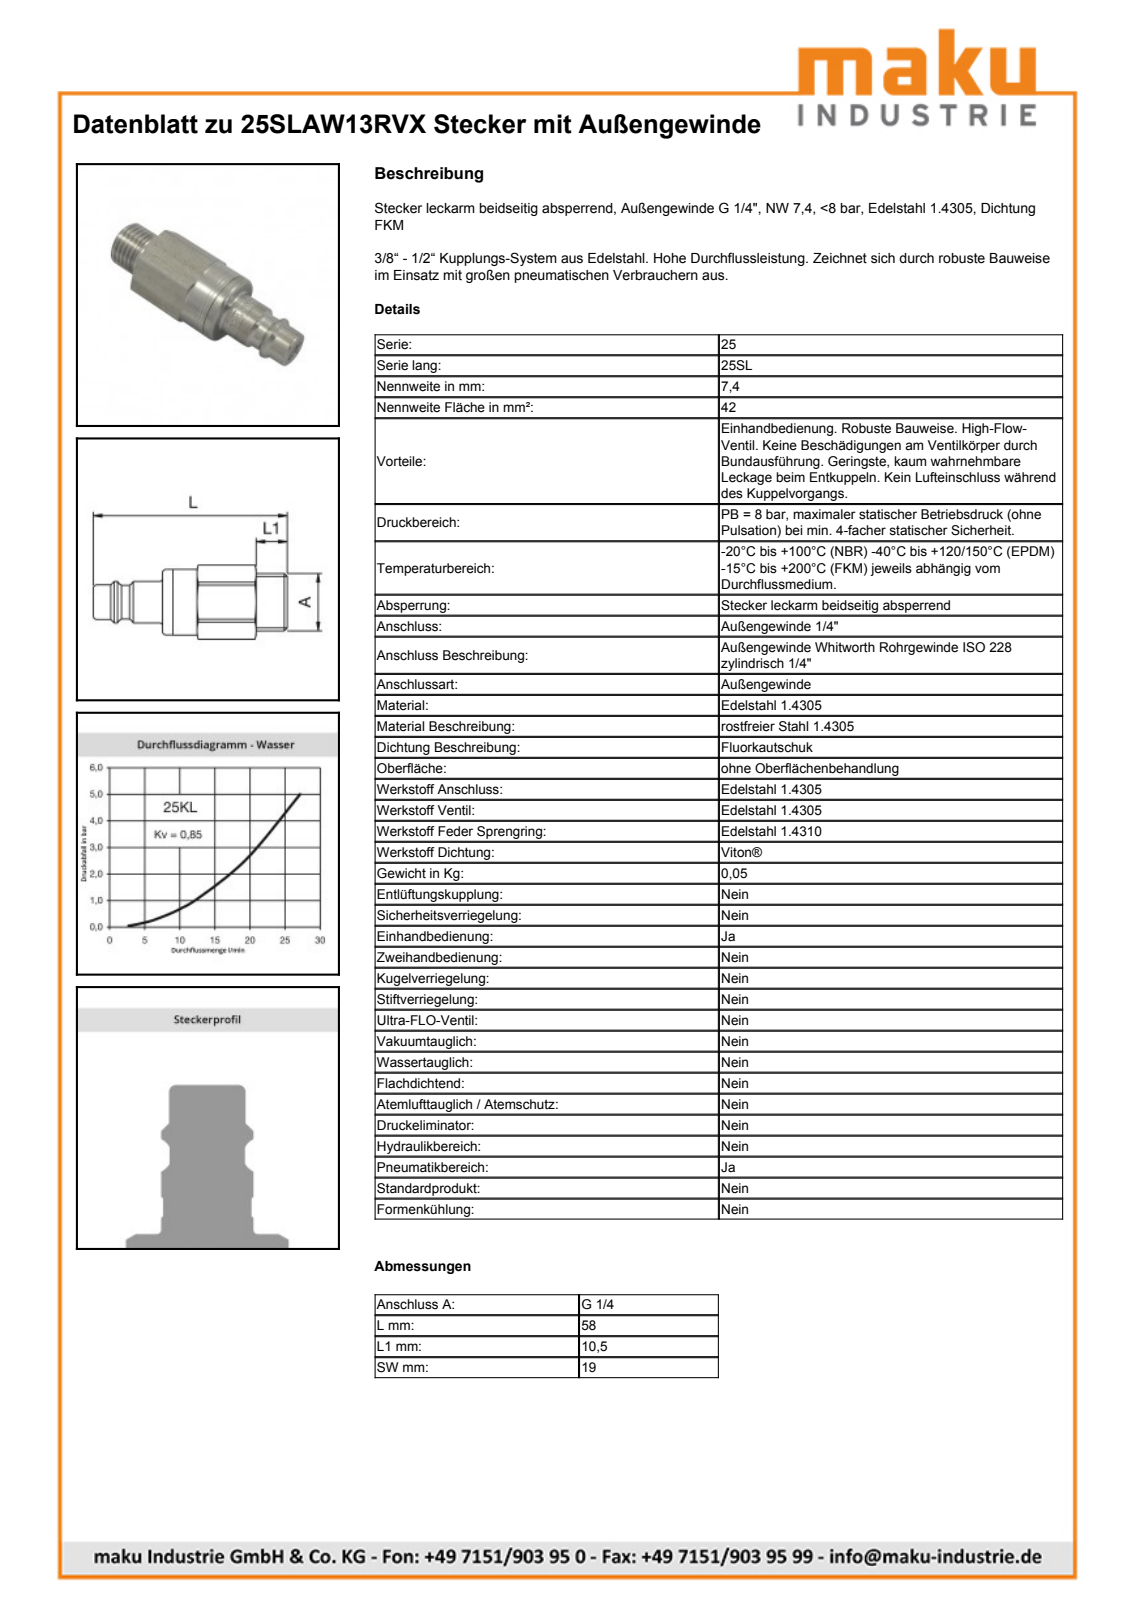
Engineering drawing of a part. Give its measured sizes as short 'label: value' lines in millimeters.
name: D105797
written by: Autodesk Inventor 2011 (AUTOMOTIVE_DESIGN)
unit: mm
bodies: 1 solid, 54 faces (15 planar, 18 cylindrical, 21 other)
size: 58 × 21.18 × 20.51
volume: 11 403 mm³; area: 3 942 mm²
holes: 1× ⌀16
bosses: 1× ⌀19, 1× ⌀18.95, 1× ⌀17, 1× ⌀15.37, 1× ⌀14.5, 1× ⌀13.16, 1× ⌀12, 1× ⌀9.9
rounds: 1× R10.7
face distances: 19, 27.5, 10.5, 38, 20, 47.5, 58, 47.1, 27.1, 0.4
